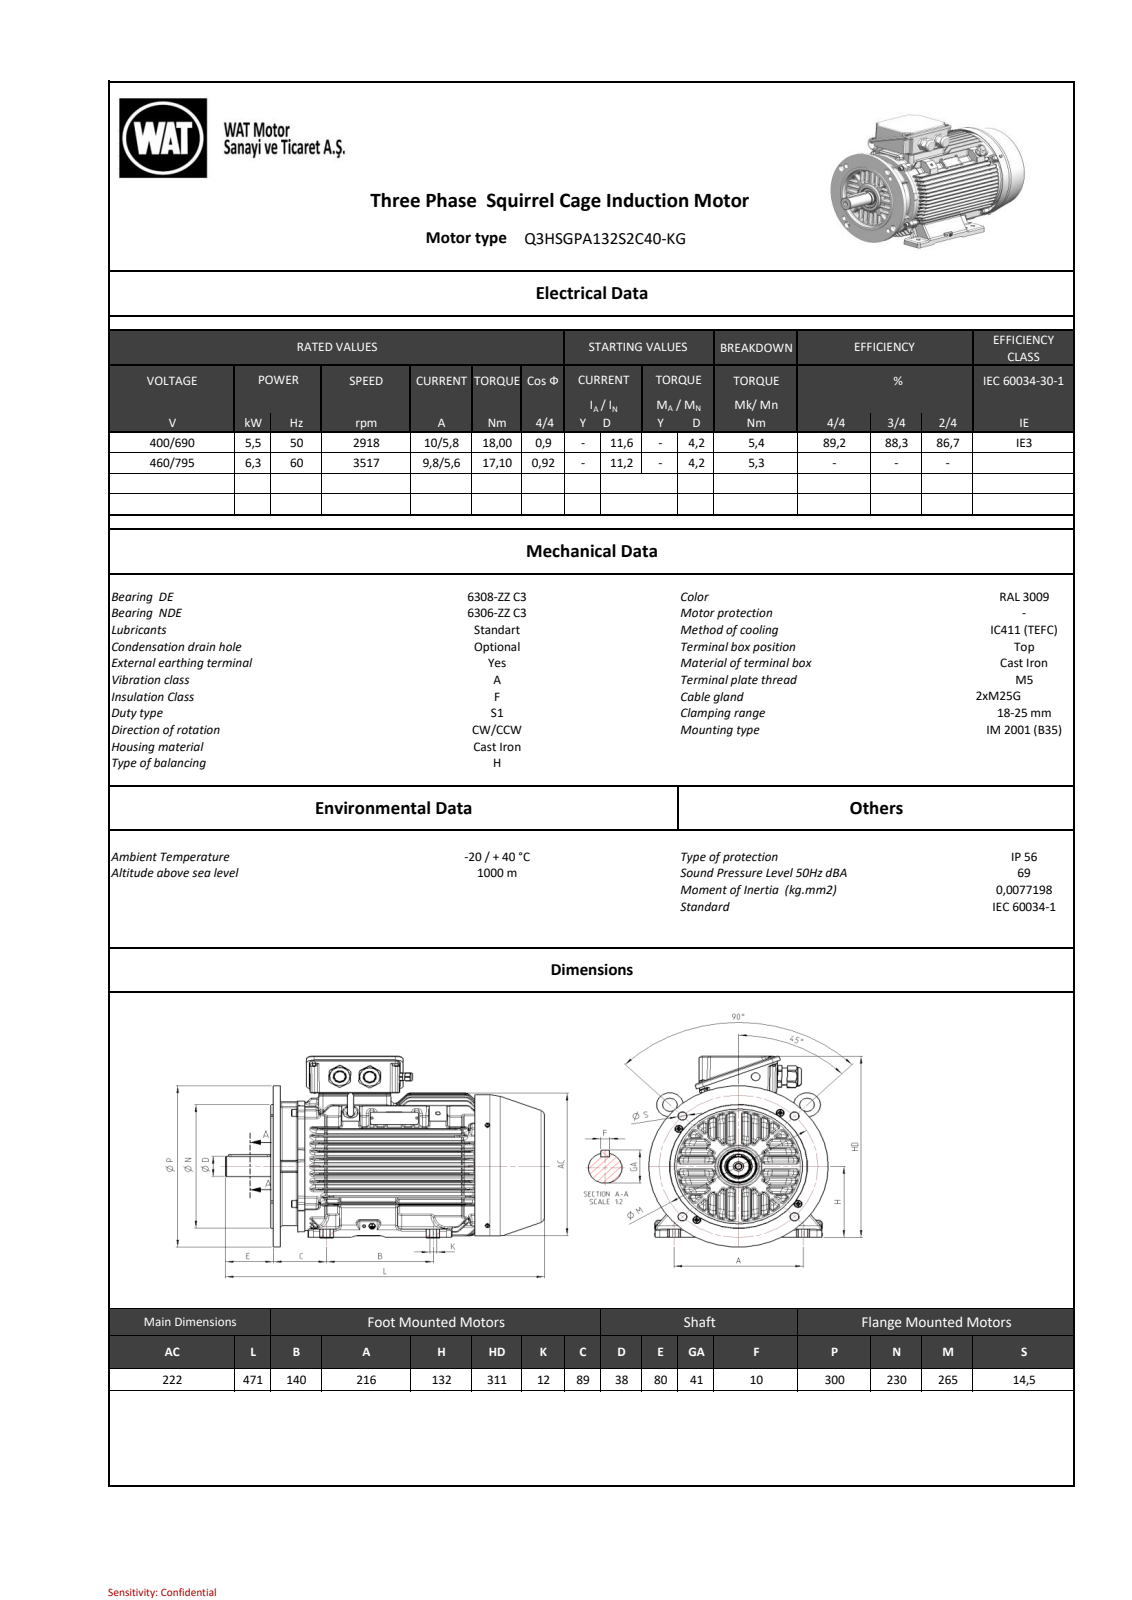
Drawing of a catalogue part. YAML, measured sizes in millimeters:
part_name: "260021E4F5C7p83w"
step_written_by: "SIEMENS PLM Software NX 11.0 (AUTOMOTIVE_DESIGN)"
units: millimeters
bodies: {solids: 0, faces: 5290, planar: 996, cylindrical: 1518, other: 2776}
overall_size: [471, 328.63, 299]
round_holes:
  - {diameter: 5, count: 9}
  - {diameter: 12, count: 4}
  - {diameter: 2.5, count: 2}
  - {diameter: 6.8, count: 2}
  - {diameter: 10, count: 2}
  - {diameter: 17.2, count: 2}
  - {diameter: 6.3, count: 1}
  - {diameter: 8, count: 1}
  - {diameter: 10.2, count: 1}
  - {diameter: 13, count: 1}
  - {diameter: 58.4, count: 1}
  - {diameter: 58.6, count: 1}
round_bosses_or_shafts:
  - {diameter: 8.65, count: 4}
  - {diameter: 8, count: 4}
  - {diameter: 4, count: 3}
  - {diameter: 27.7, count: 2}
  - {diameter: 25.25, count: 2}
  - {diameter: 20, count: 2}
  - {diameter: 299, count: 1}
  - {diameter: 230, count: 1}
partial_cylinders:
  - {radius: 4, count: 331}
  - {radius: 3, count: 132}
  - {radius: 1.5, count: 96}
  - {radius: 0.5, count: 93}
  - {radius: 2, count: 49}
  - {radius: 6, count: 28}
  - {radius: 1, count: 25}
  - {radius: 1.8, count: 24}
face_to_face_distances: [6, 51, 6.5, 13.1, 13.18, 26.28, 39.54, 26.44, 13.26, 39.96]
hole_center_spacings: [97, 137.18, 33.69, 111.28, 158.92, 191.06, 194.01, 27.5]
